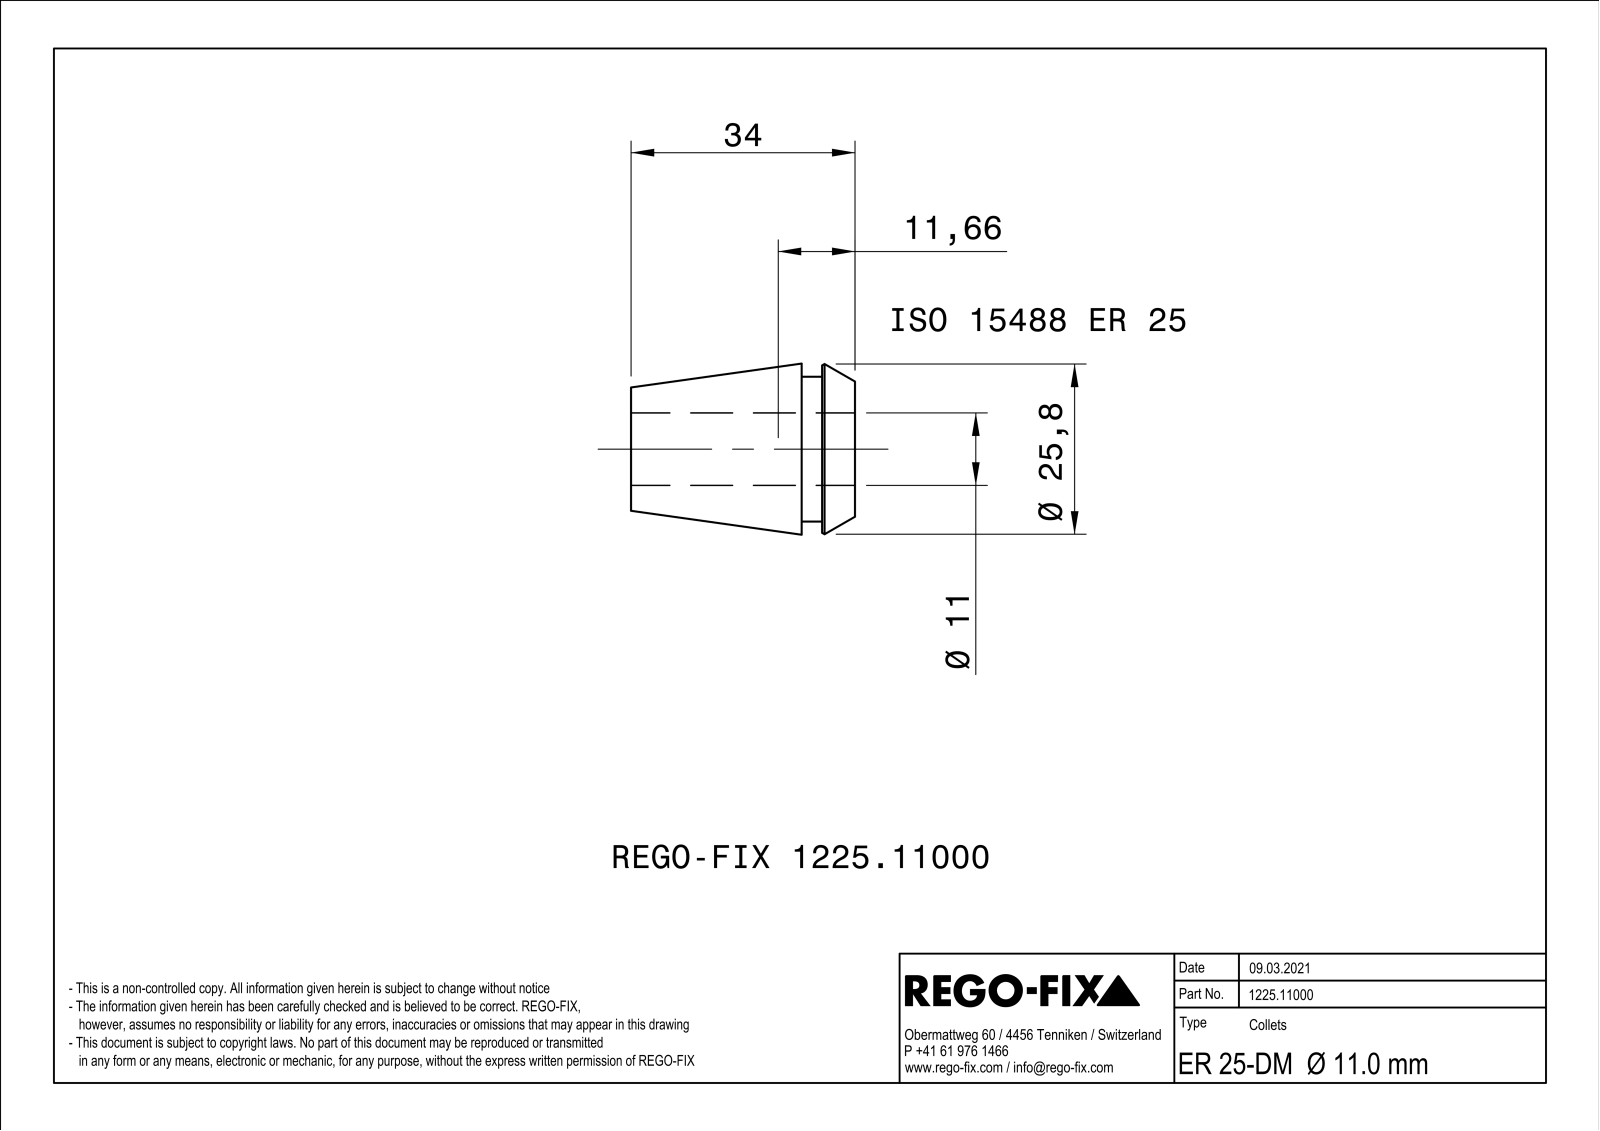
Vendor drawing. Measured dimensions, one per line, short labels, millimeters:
name: NOCUT
written by: SIEMENS PLM Software Solid Edge ST10 (AUTOMOTIVE_DESIGN)
unit: mm
bodies: 1 solid, 154 faces (80 planar, 9 cylindrical, 65 other)
size: 34 × 25.99 × 25.99
volume: 8 617 mm³; area: 8 062 mm²
holes: 1× ⌀11
bosses: 1× ⌀22
face distances: 0.8, 34, 5, 29, 8.1, 25.9, 3.1, 15, 10, 6.9
